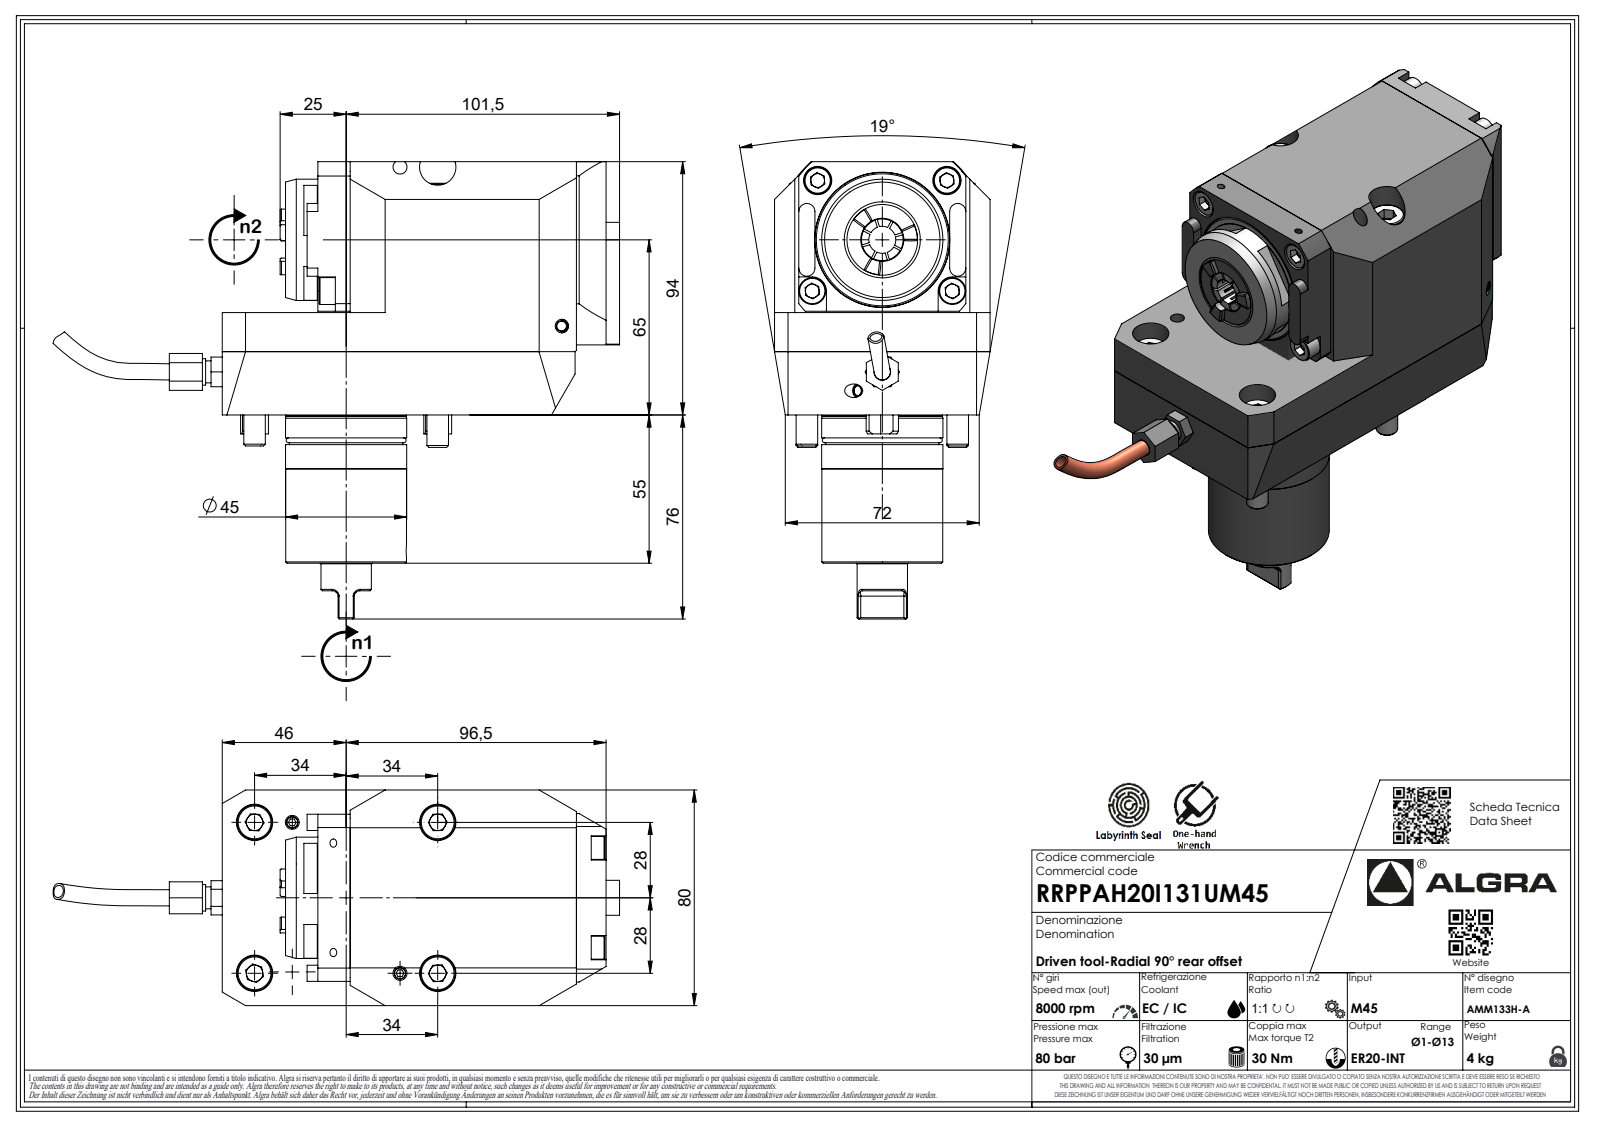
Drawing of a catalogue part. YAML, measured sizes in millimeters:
part_name: "RRPPAH20I131UM45"
step_written_by: "SolidWorks 2023 (AUTOMOTIVE_DESIGN)"
units: millimeters
bodies: {solids: 1, faces: 548, planar: 371, cylindrical: 81, other: 96}
overall_size: [210.29, 169.7, 80]
volume: 928332
surface_area: 72814
round_holes:
  - {diameter: 13.5, count: 2}
  - {diameter: 2.1, count: 1}
round_bosses_or_shafts:
  - {diameter: 8, count: 4}
  - {diameter: 45, count: 2}
  - {diameter: 13, count: 2}
  - {diameter: 44.85, count: 1}
  - {diameter: 44.6, count: 1}
  - {diameter: 42, count: 1}
  - {diameter: 18.7, count: 1}
  - {diameter: 9.8, count: 1}
partial_cylinders:
  - {radius: 0.33, count: 7}
  - {radius: 0.52, count: 7}
  - {radius: 3.7, count: 7}
  - {radius: 2, count: 6}
  - {radius: 3, count: 4}
  - {radius: 4, count: 4}
  - {radius: 10, count: 3}
  - {radius: 6, count: 2}
face_to_face_distances: [94, 56, 38, 80, 142.5, 37.8, 93.8, 12, 23.5, 119]
hole_center_spacings: [56]
